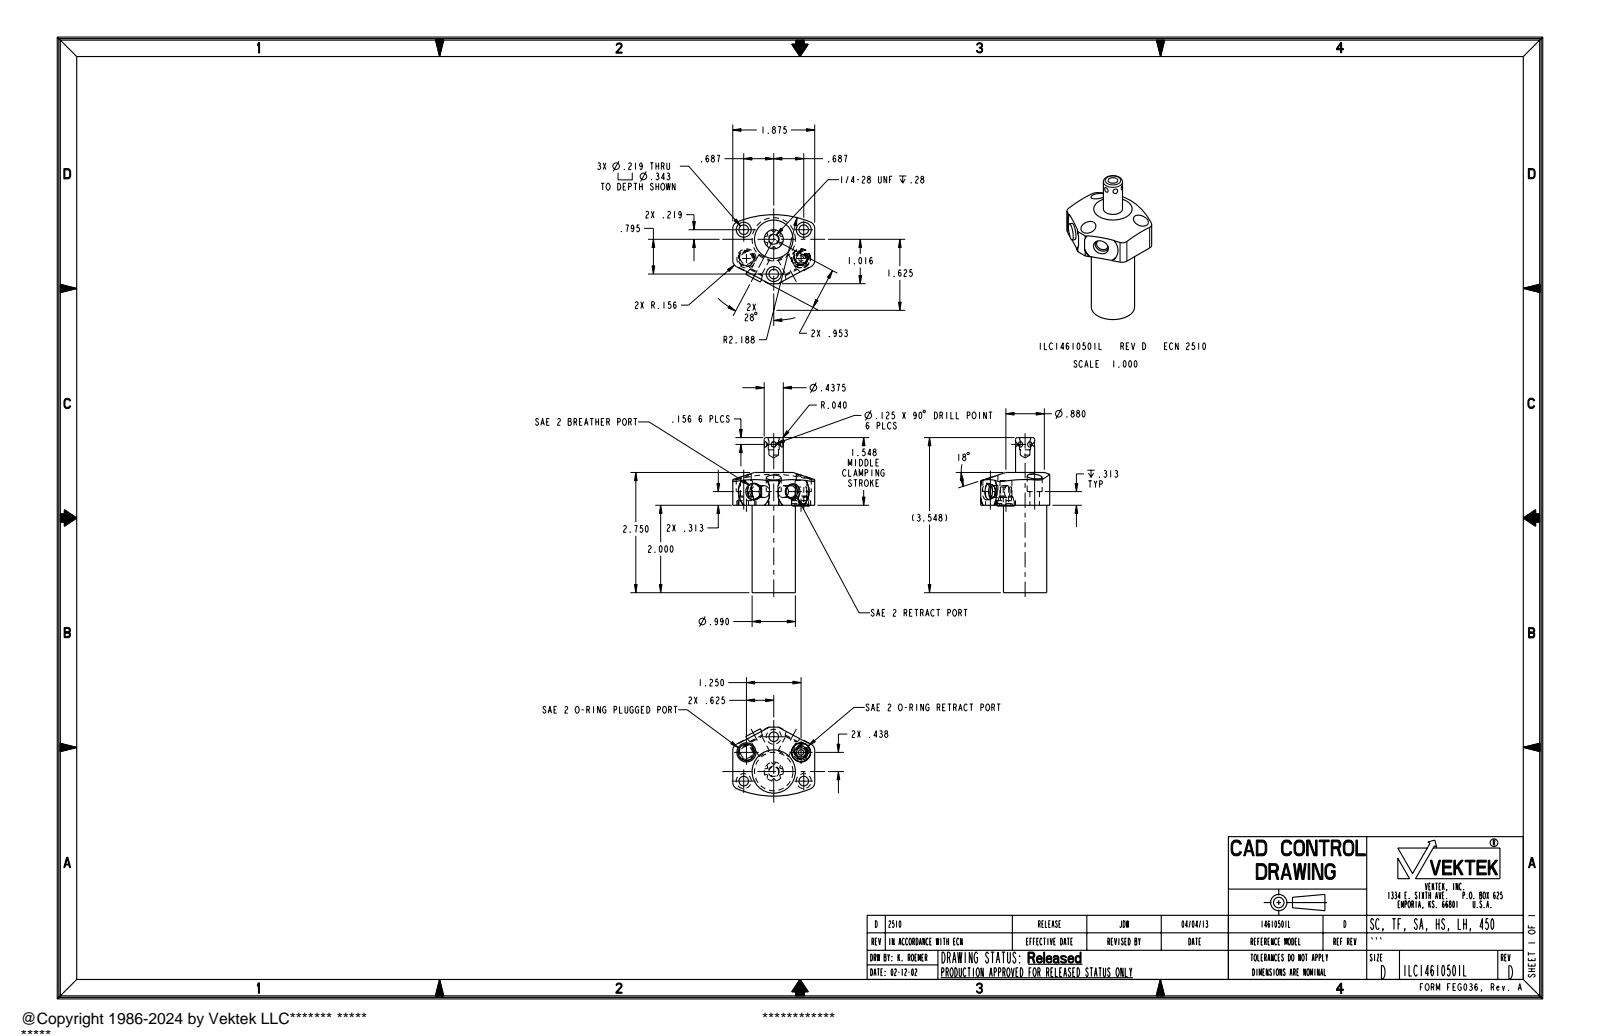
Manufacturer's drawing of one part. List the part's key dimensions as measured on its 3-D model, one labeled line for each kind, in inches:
Part name (STEP PRODUCT): ILC14610501L
STEP written by: PRO/ENGINEER BY PARAMETRIC TECHNOLOGY CORPORATION, 2007460 (AUTOMOTIVE_DESIGN_CC2)
Units: inches
Bodies: 1 solid, 127 faces (34 planar, 55 cylindrical, 38 other)
Overall size (bounding box): 3.548 × 1.875 × 1.579
Volume: 3.076 in³ · Surface area: 21.1 in²
Round holes (diameter × count): ⌀0.272 ×4, ⌀0.219 ×3, ⌀0.343 ×3, ⌀0.438 ×2, ⌀0.125 ×1, ⌀0.221 ×1
Round bosses / shafts (diameter × count): ⌀0.378 ×2, ⌀0.99 ×1, ⌀0.437 ×1, ⌀0.43 ×1, ⌀0.256 ×1, ⌀0.25 ×1, ⌀0.21 ×1
Partial cylindrical surfaces — rounded edges, fillets, slot ends (radius × count): R0.156 ×4, R0.412 ×2, R2.188 ×1
Main face-to-face distances: 2, 2.75, 0.75, 1.875, 0.105, 0.313, 2.105, 0.645, 2.313, 0.208
Hole centre spacings: 0.66, 0.72, 0.721, 0.763, 1.225, 1.468, 0.795, 1.25
